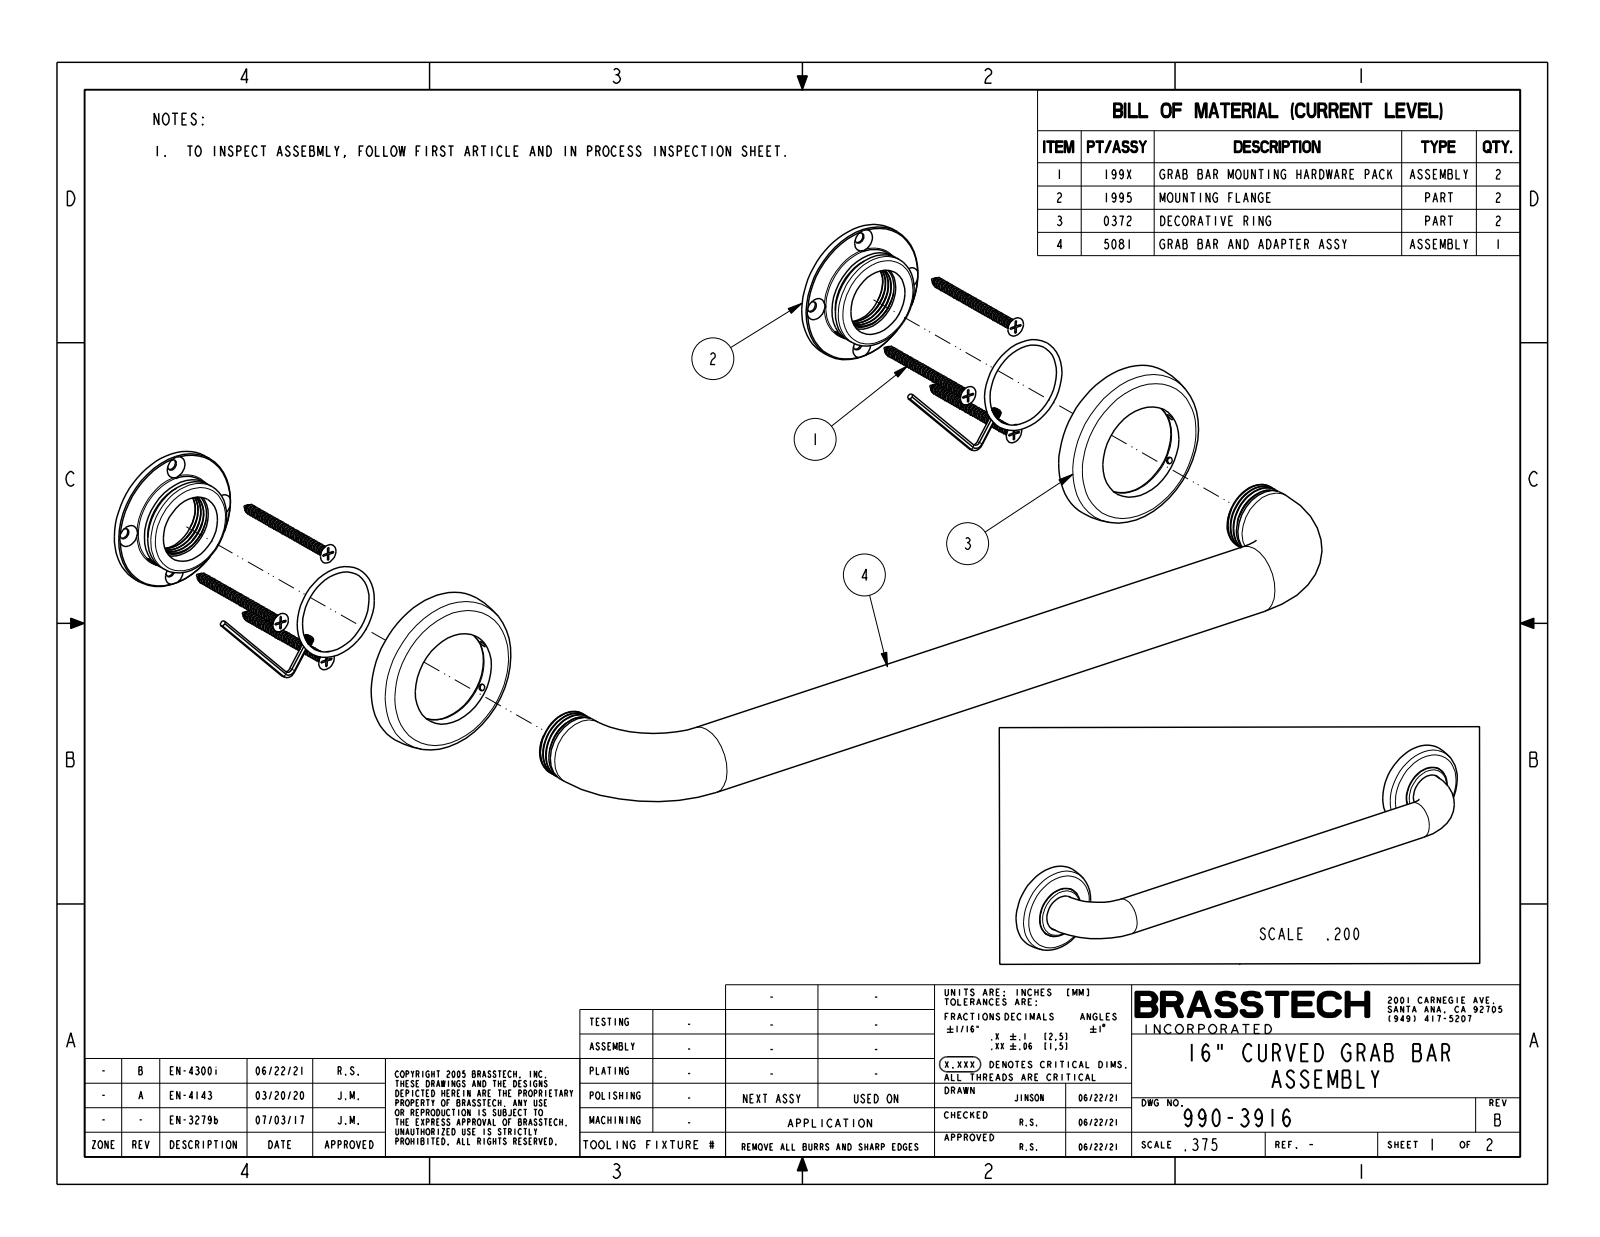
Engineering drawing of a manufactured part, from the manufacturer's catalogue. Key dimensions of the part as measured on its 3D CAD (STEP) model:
Part name (STEP PRODUCT): 91496; 1995; 20-287_ASM; 80527 (+4 more)
STEP written by: PRO/ENGINEER BY PARAMETRIC TECHNOLOGY CORPORATION, 2013150 (CONFIG_CONTROL_DESIGN)
Units: inches
Bodies: 9 solids, 760 faces (228 planar, 200 cylindrical, 332 other)
Overall size (bounding box): 19 × 3 × 2.912
Volume: 7.625 in³ · Surface area: 327.8 in²
Round holes (diameter × count): ⌀0.202 ×8, ⌀0.1 ×4, ⌀1.152 ×3, ⌀0.163 ×2, ⌀0.866 ×2, ⌀1.16 ×2, ⌀1.26 ×2, ⌀1.77 ×2
Round bosses / shafts (diameter × count): ⌀1.75 ×4, ⌀0.126 ×4, ⌀1.25 ×3, ⌀2.6 ×2, ⌀1.928 ×2, ⌀1.594 ×2, ⌀1.237 ×2, ⌀1.147 ×2
Partial cylindrical surfaces — rounded edges, fillets, slot ends (radius × count): R0.212 ×8, R0.038 ×4, R0.025 ×2
Main face-to-face distances: 0.15, 0.45, 0.6, 0.074, 0.076, 0.526, 0.1, 0.35, 0.25, 0.05
Hole centre spacings: 1.087, 1.538, 16, 2.175, 14.952, 16.037, 17.122, 0.084
